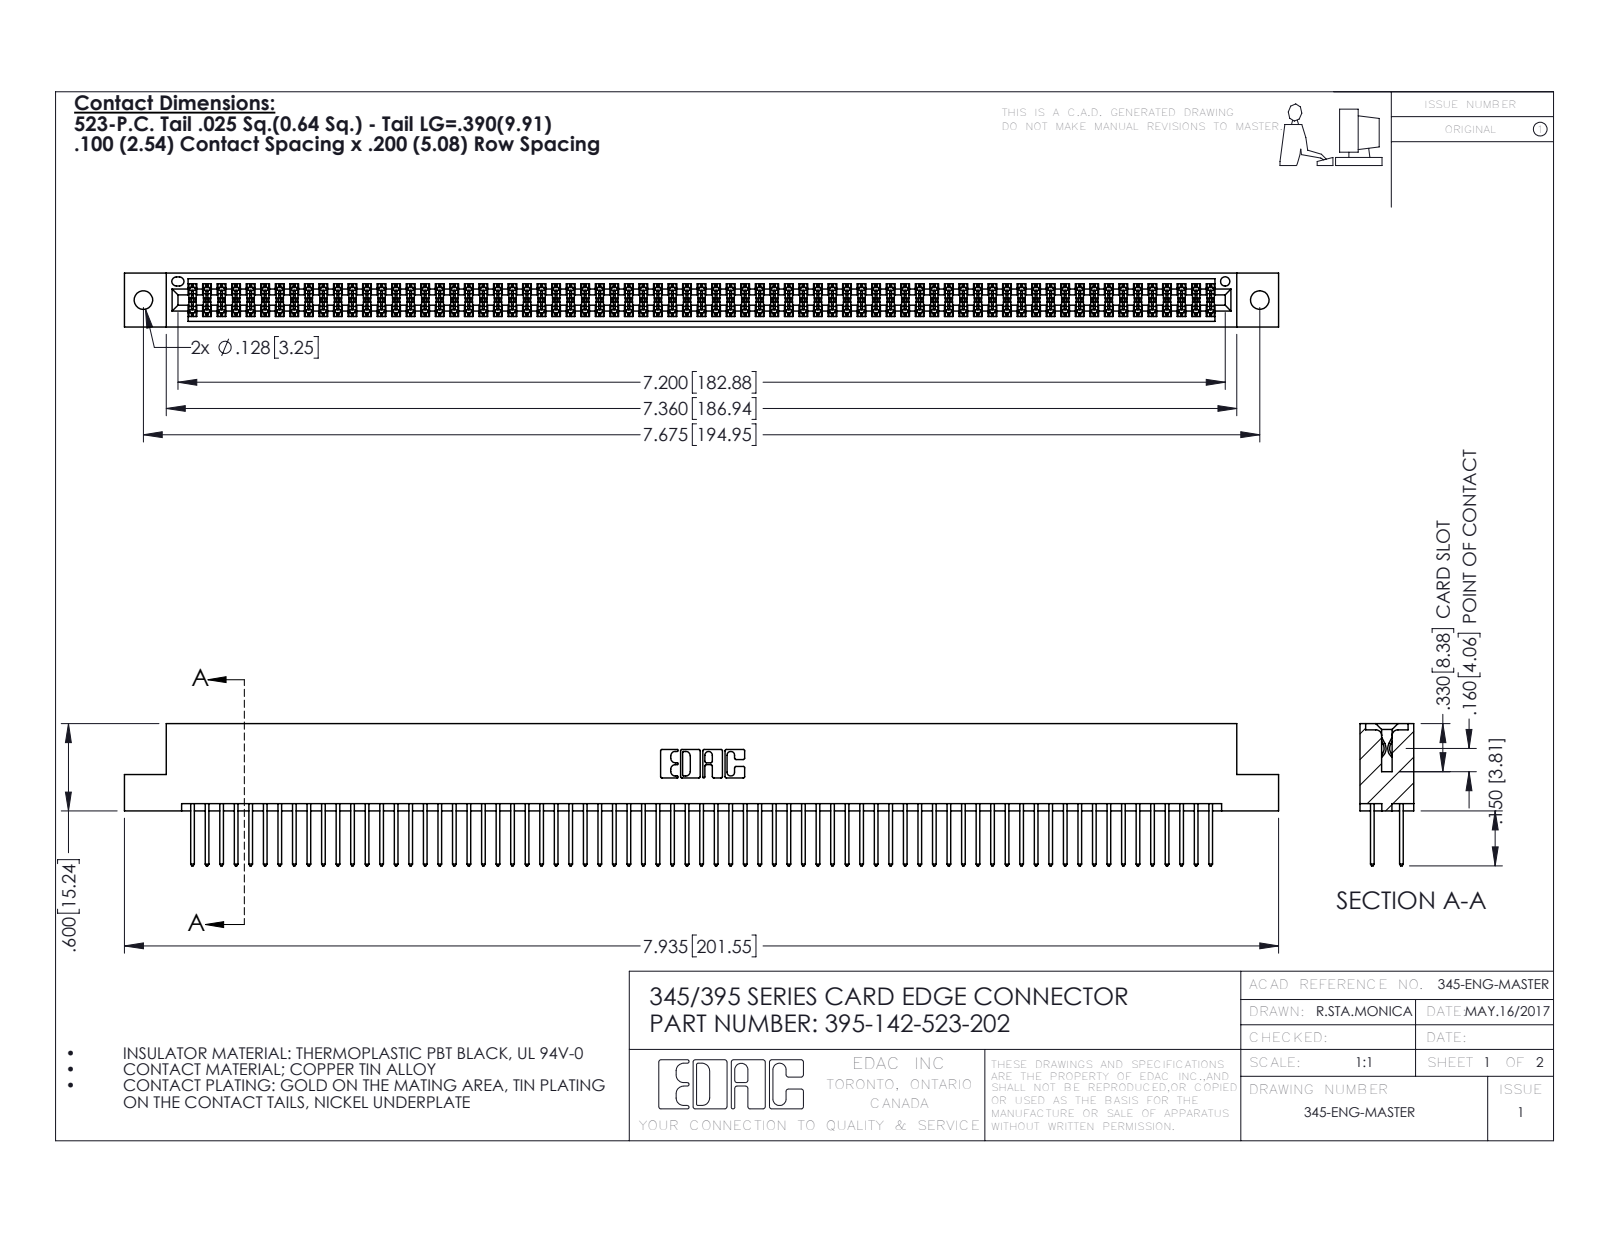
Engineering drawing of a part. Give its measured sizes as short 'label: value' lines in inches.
name: 345 Part_Flush Mounting Lugs - 0.128 Dia; 345-292-001_345-293-123; 395-142-523-202
written by: SolidWorks 2016 (CONFIG_CONTROL_DESIGN)
unit: in
bodies: 143 solids, 7226 faces (4766 planar, 2460 cylindrical, 0 other)
size: 7.935 × 0.977 × 0.37
volume: 1.227 in³; area: 48.53 in²
holes: 2× ⌀0.128, 1× ⌀0.064
rounds: 213× R0.006, 142× R0.01, 22× R0.01, 6× R0.007, 6× R0.031, 3× R0.026, 2× R0.014, 2× R0.019
face distances: 0.298, 0.072, 0.2, 0.098, 0.272, 0.025, 0.37, 0.225, 0.175, 0.149
hole spacings: 0.27, 7.439, 7.675
